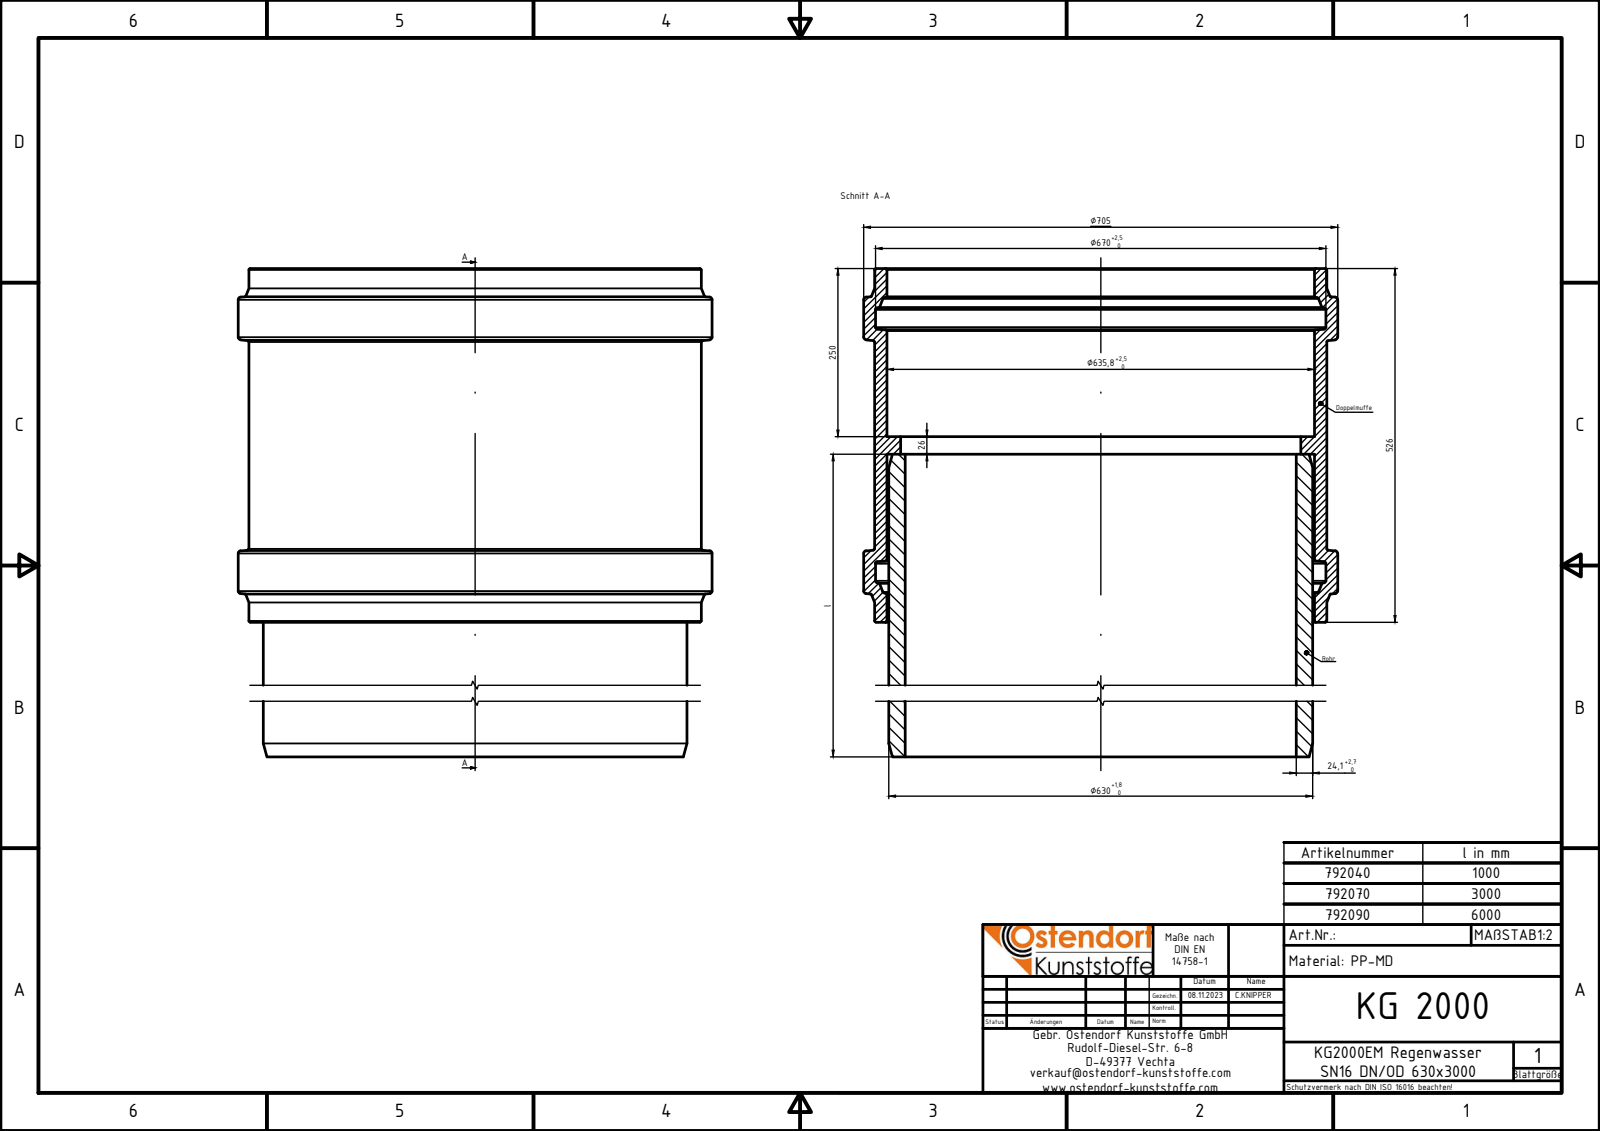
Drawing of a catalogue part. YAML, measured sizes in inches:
part_name: "792070z"
step_written_by: "Autodesk Inventor 2024 (AUTOMOTIVE_DESIGN)"
units: inches
bodies: {solids: 1, faces: 60, planar: 6, cylindrical: 14, other: 40}
overall_size: [128.976, 27.748, 27.748]
volume: 9776
surface_area: 21650
round_holes:
  - {diameter: 22.906, count: 1}
  - {diameter: 23.417, count: 1}
  - {diameter: 25.031, count: 1}
  - {diameter: 26.378, count: 1}
round_bosses_or_shafts:
  - {diameter: 27.748, count: 1}
  - {diameter: 26.48, count: 1}
  - {diameter: 24.803, count: 1}
face_to_face_distances: [10.866, 9.843, 119.134, 108.268, 128.976, 20.709, 118.11, 1.024]
